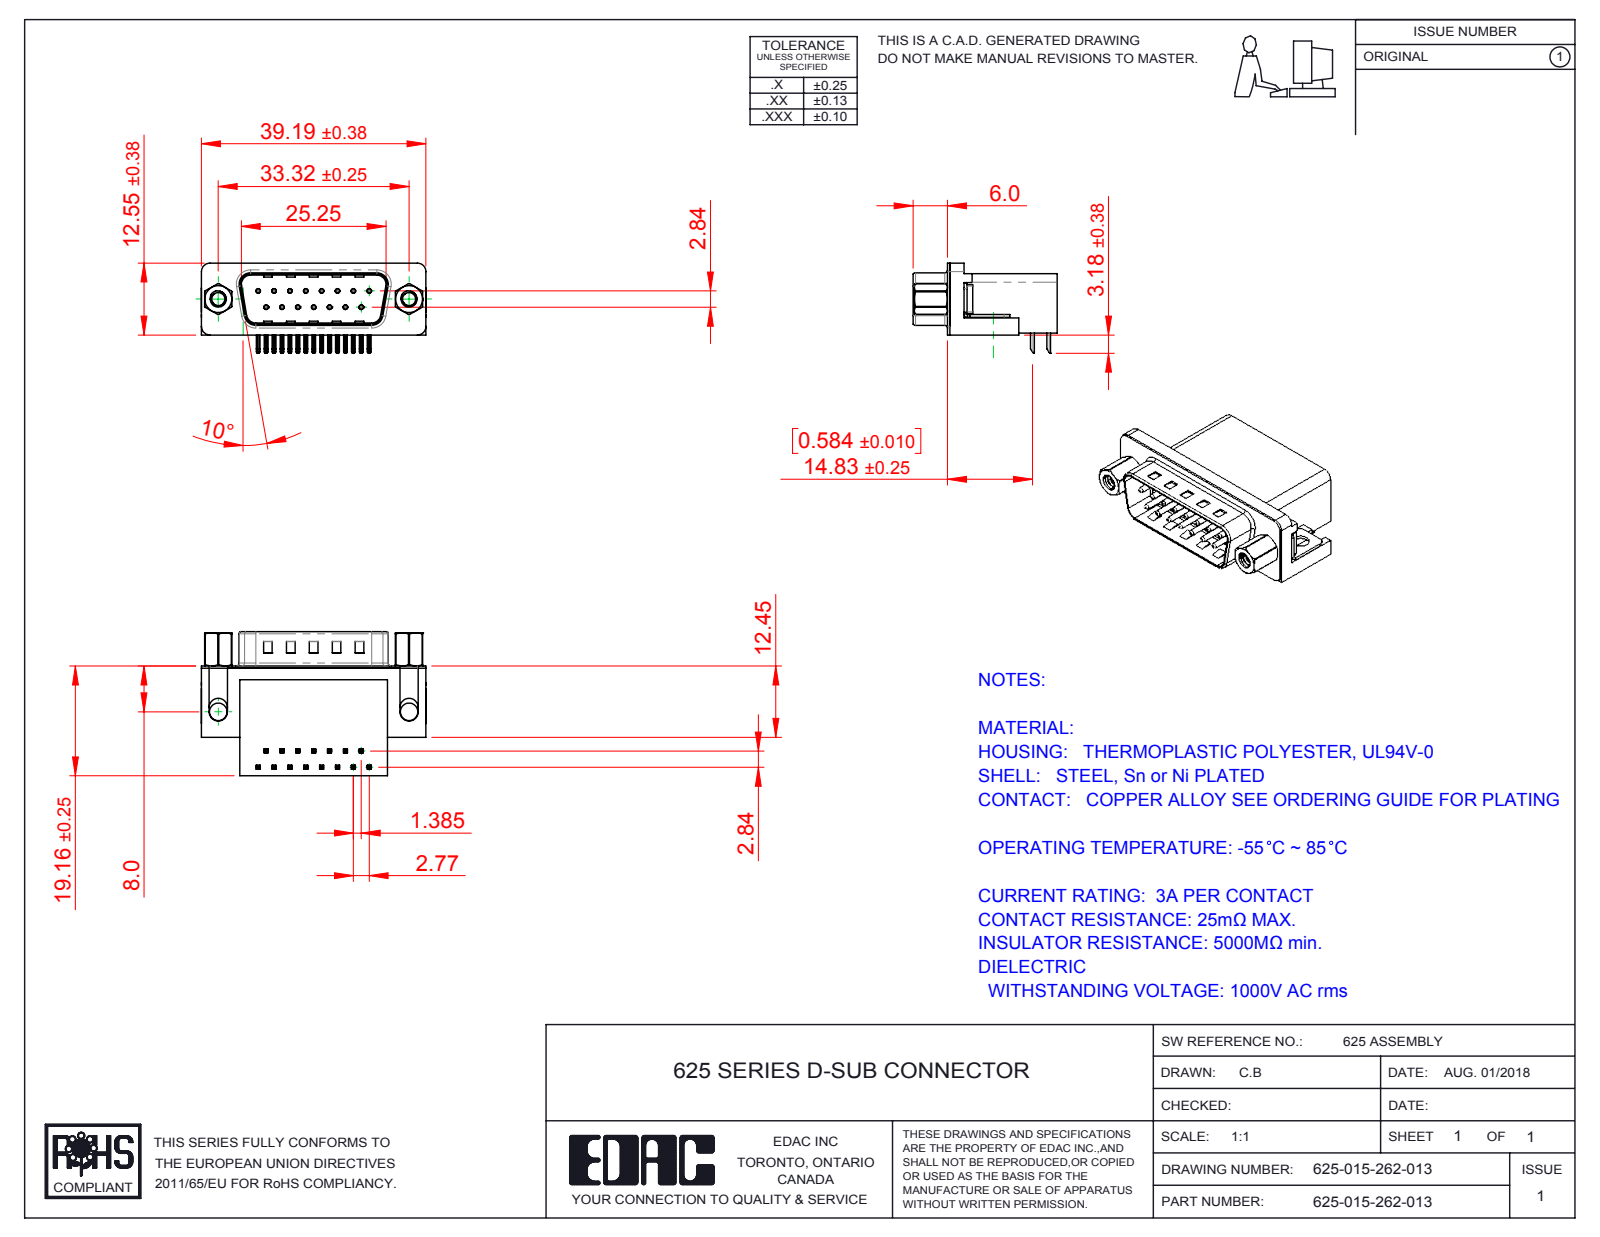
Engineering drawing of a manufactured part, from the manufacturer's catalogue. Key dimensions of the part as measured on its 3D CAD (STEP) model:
Part name (STEP PRODUCT): 625-015-262-013; 625 Contact Top; 625 Housing_15 Socket; 625 Contact Bottom (+4 more)
STEP written by: SolidWorks 2016 (CONFIG_CONTROL_DESIGN)
Units: millimetres
Bodies: 23 solids, 1605 faces (915 planar, 519 cylindrical, 171 other)
Overall size (bounding box): 39.22 × 25.16 × 15.73
Volume: 6 454 mm³ · Surface area: 6 895 mm²
Round holes (diameter × count): ⌀0.35 ×15, ⌀0.8 ×15, ⌀2.26 ×2, ⌀2.29 ×2, ⌀3.05 ×2, ⌀4 ×2, ⌀4.8 ×2, ⌀5 ×2
Round bosses / shafts (diameter × count): ⌀0.75 ×15, ⌀4.9 ×2, ⌀4.75 ×2, ⌀3.9 ×2, ⌀2.79 ×2
Partial cylindrical surfaces — rounded edges, fillets, slot ends (radius × count): R0.25 ×68, R0.12 ×30, R1 ×16, R0.5 ×9, R1.6 ×8, R1.5 ×6, R0.9 ×4, R2 ×4
Main face-to-face distances: 0.4, 10.35, 18.76, 2.1, 19.16, 10.46, 1.7, 10.86, 8.76, 16.26
Hole centre spacings: 3.16, 2.77, 5.54, 8.31, 11.08, 5.03, 5.04, 7.48
